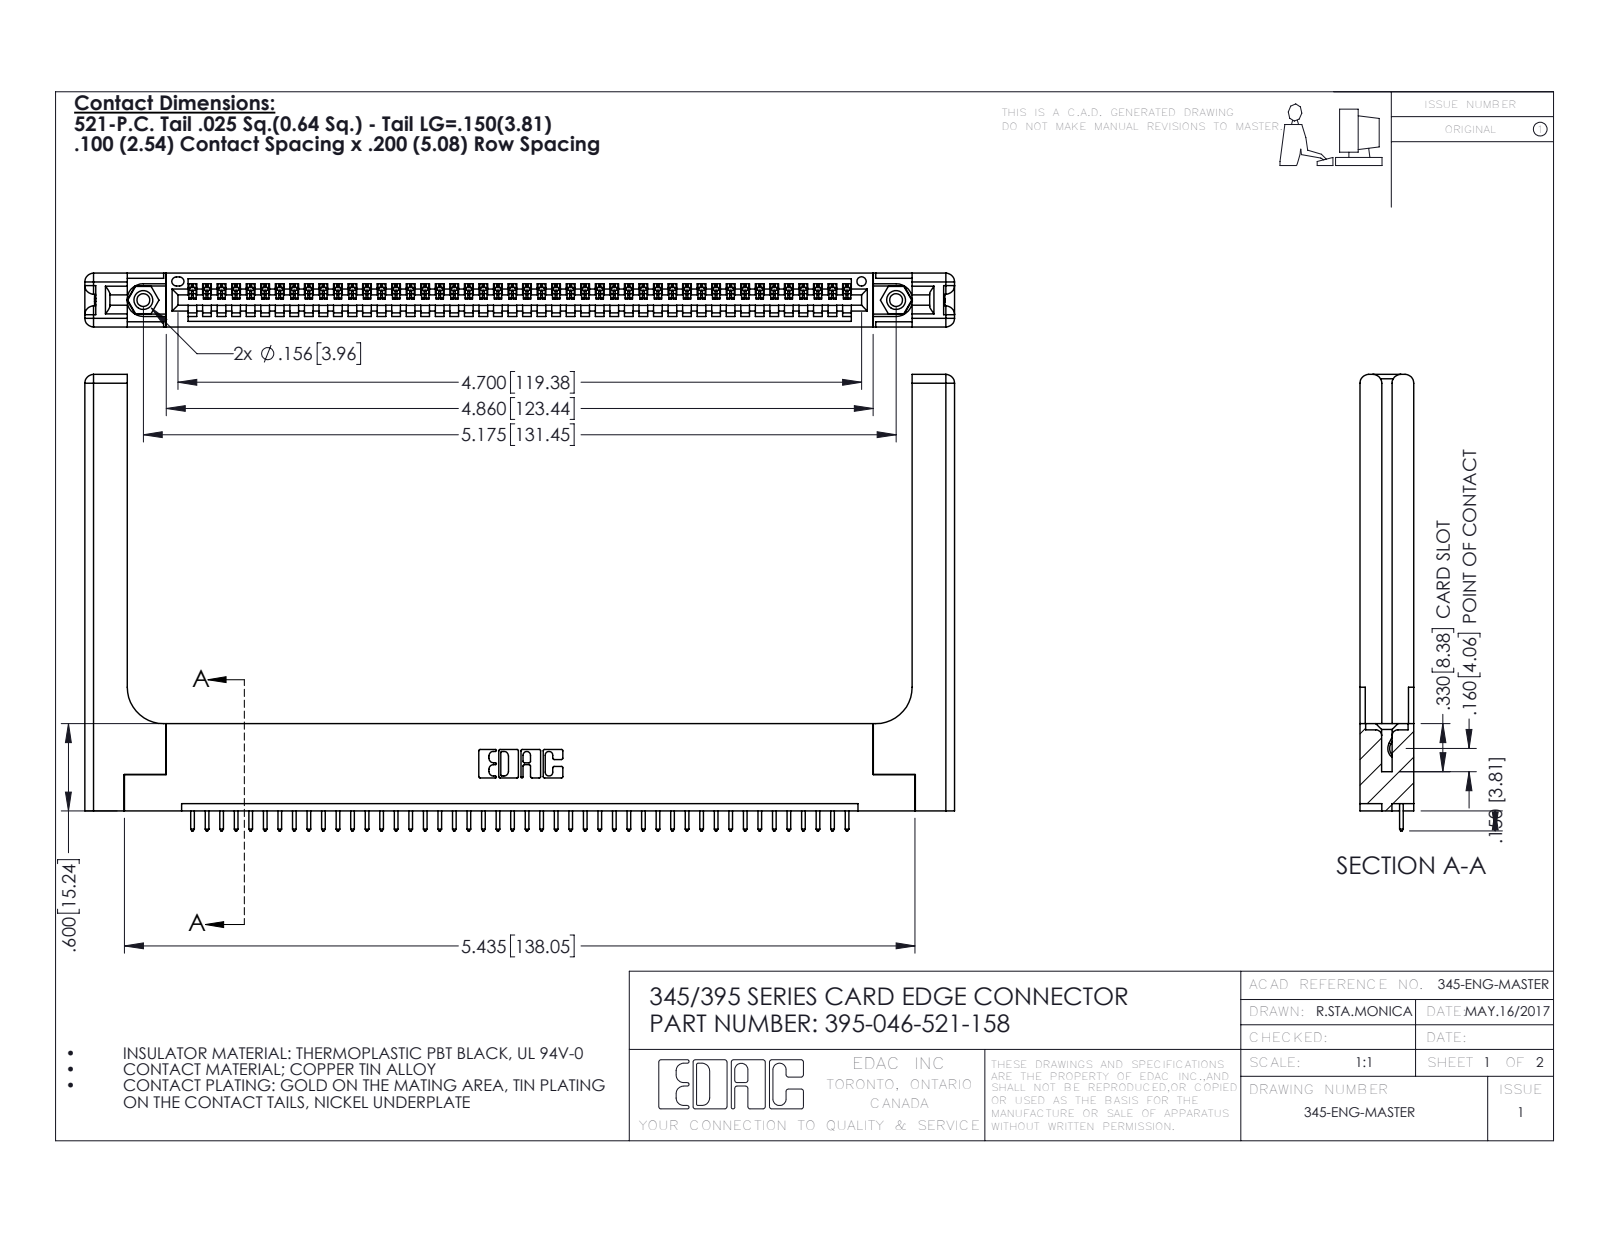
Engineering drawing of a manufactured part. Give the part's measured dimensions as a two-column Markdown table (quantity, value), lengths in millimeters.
| quantity | value |
| --- | --- |
| part name | 345-250-001_345-250-001-102; 345-220-058_345-220-058; 345 Part_Flush Mounting Lugs - 0.156 Dia-TH; 345-292-001_345-293-121 (+1 more) |
| STEP written by | SolidWorks 2016 (CONFIG_CONTROL_DESIGN) |
| units | millimeters |
| bodies | 51 solids, 3050 faces (2068 planar, 922 cylindrical, 60 other) |
| overall size | 151.9 × 79.7 × 9.4 |
| volume | 22 830 mm³ |
| surface area | 23 880 mm² |
| round holes (diameter × count) | 2.3 × 2, 3.2 × 2, 4 × 2, 1.6 × 1 |
| round bosses / shafts (diameter × count) | 3.9 × 2 |
| partial cylindrical surfaces (radius × count) | 0.2 × 92, 0.3 × 92, 0.3 × 22, 1.5 × 16, 0.2 × 6, 0.8 × 6, 0.7 × 3, 0.8 × 2 |
| main face-to-face distances | 9.4, 1.8, 7.6, 5.1, 2.5, 6.9, 0.6, 5.7, 3.8, 3.8 |
| hole center spacings | 6.9, 125.5, 131.4 |
